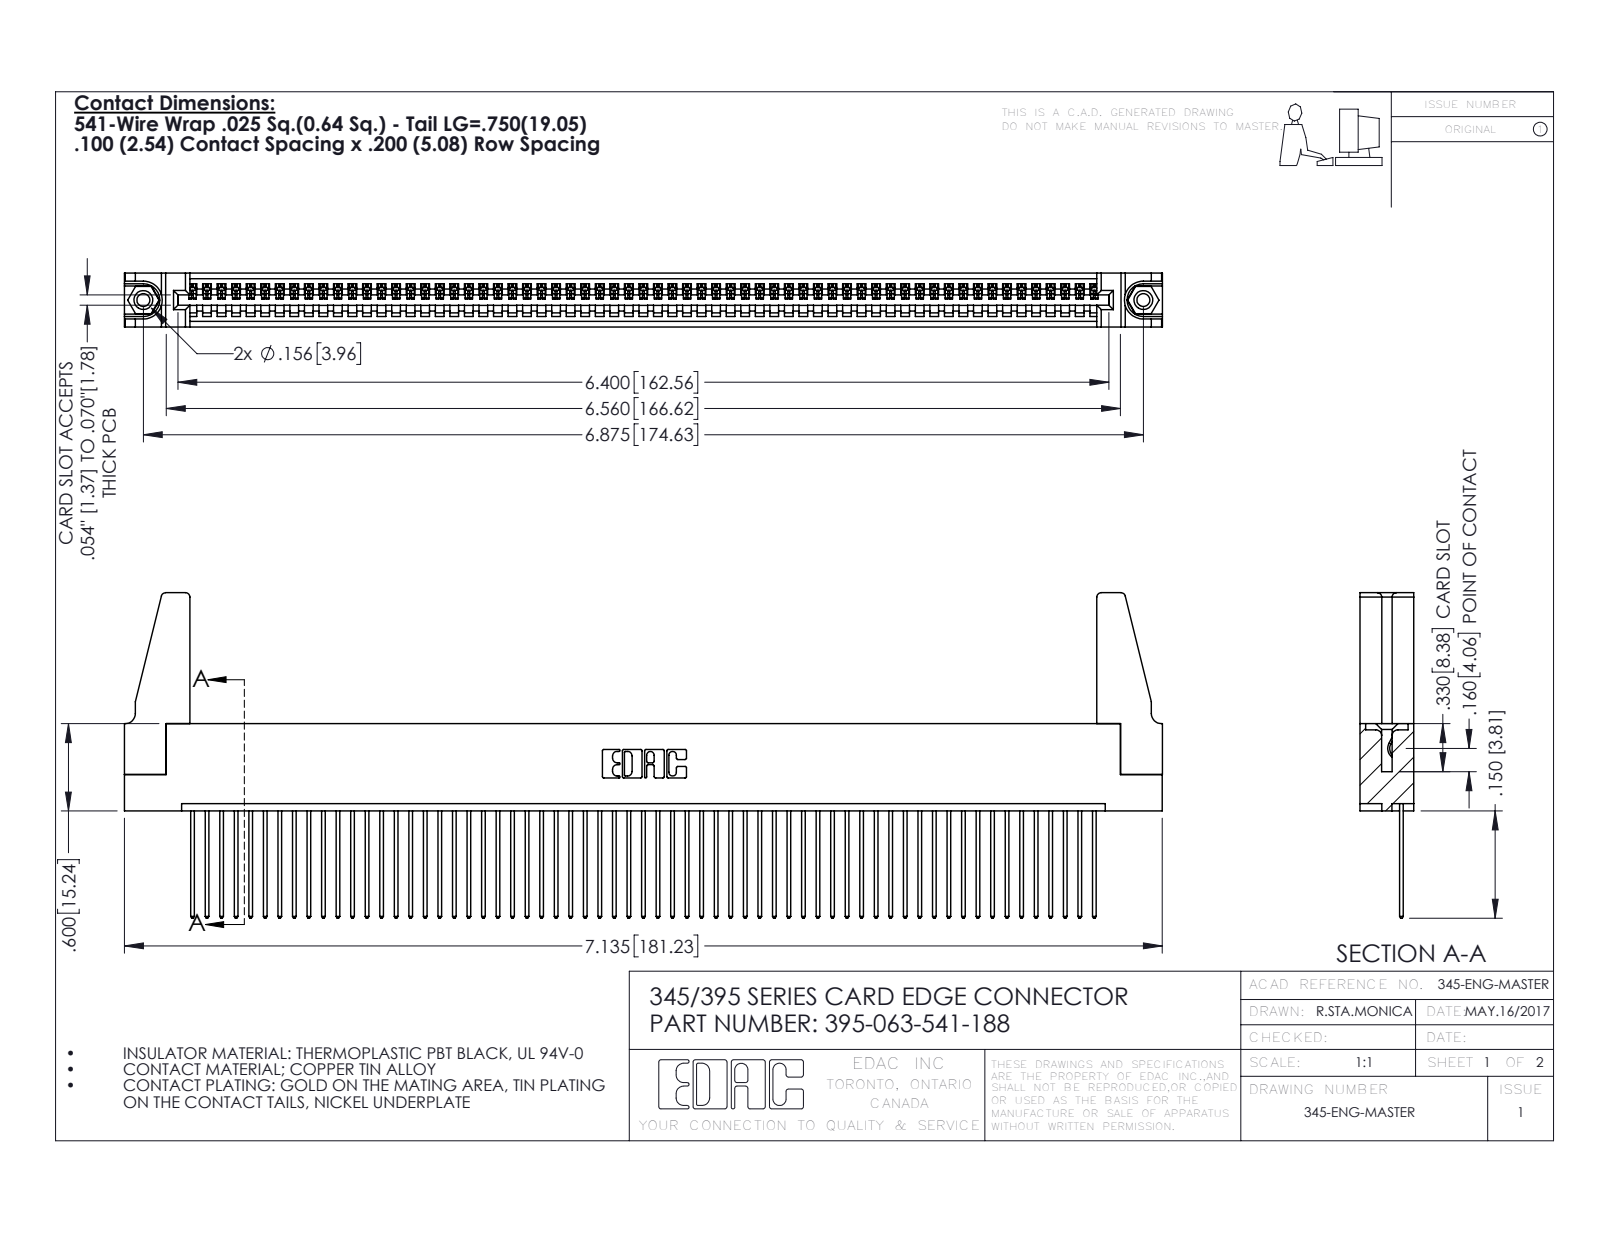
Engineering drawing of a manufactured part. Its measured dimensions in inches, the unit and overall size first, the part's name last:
Units: inches
Overall size (bounding box): 7.136 × 2.237 × 0.37
Round holes (diameter × count): ⌀0.089 ×2, ⌀0.125 ×2, ⌀0.156 ×2, ⌀0.064 ×1
Round bosses / shafts (diameter × count): ⌀0.155 ×2
Partial cylindrical surfaces — rounded edges, fillets, slot ends (radius × count): R0.006 ×126, R0.01 ×126, R0.01 ×22, R0.03 ×8, R0.007 ×6, R0.031 ×6, R0.026 ×3, R0.031 ×2
Main face-to-face distances: 0.072, 0.298, 0.37, 0.098, 0.272, 0.025, 0.2, 0.225, 0.149, 0.072
Hole centre spacings: 0.27, 6.639, 6.875
Volume: 1.272 in³ · Surface area: 43.43 in²
Bodies: 68 solids, 3904 faces (2672 planar, 1216 cylindrical, 16 other)
Part name (STEP PRODUCT): 395-063-541-188; 345-292-001_345-293-141; 345 Part_Flush Mounting Lugs - 0.156 Dia-TH; 345-220-078_345-220-088 (+1 more)
STEP written by: SolidWorks 2016 (CONFIG_CONTROL_DESIGN)
